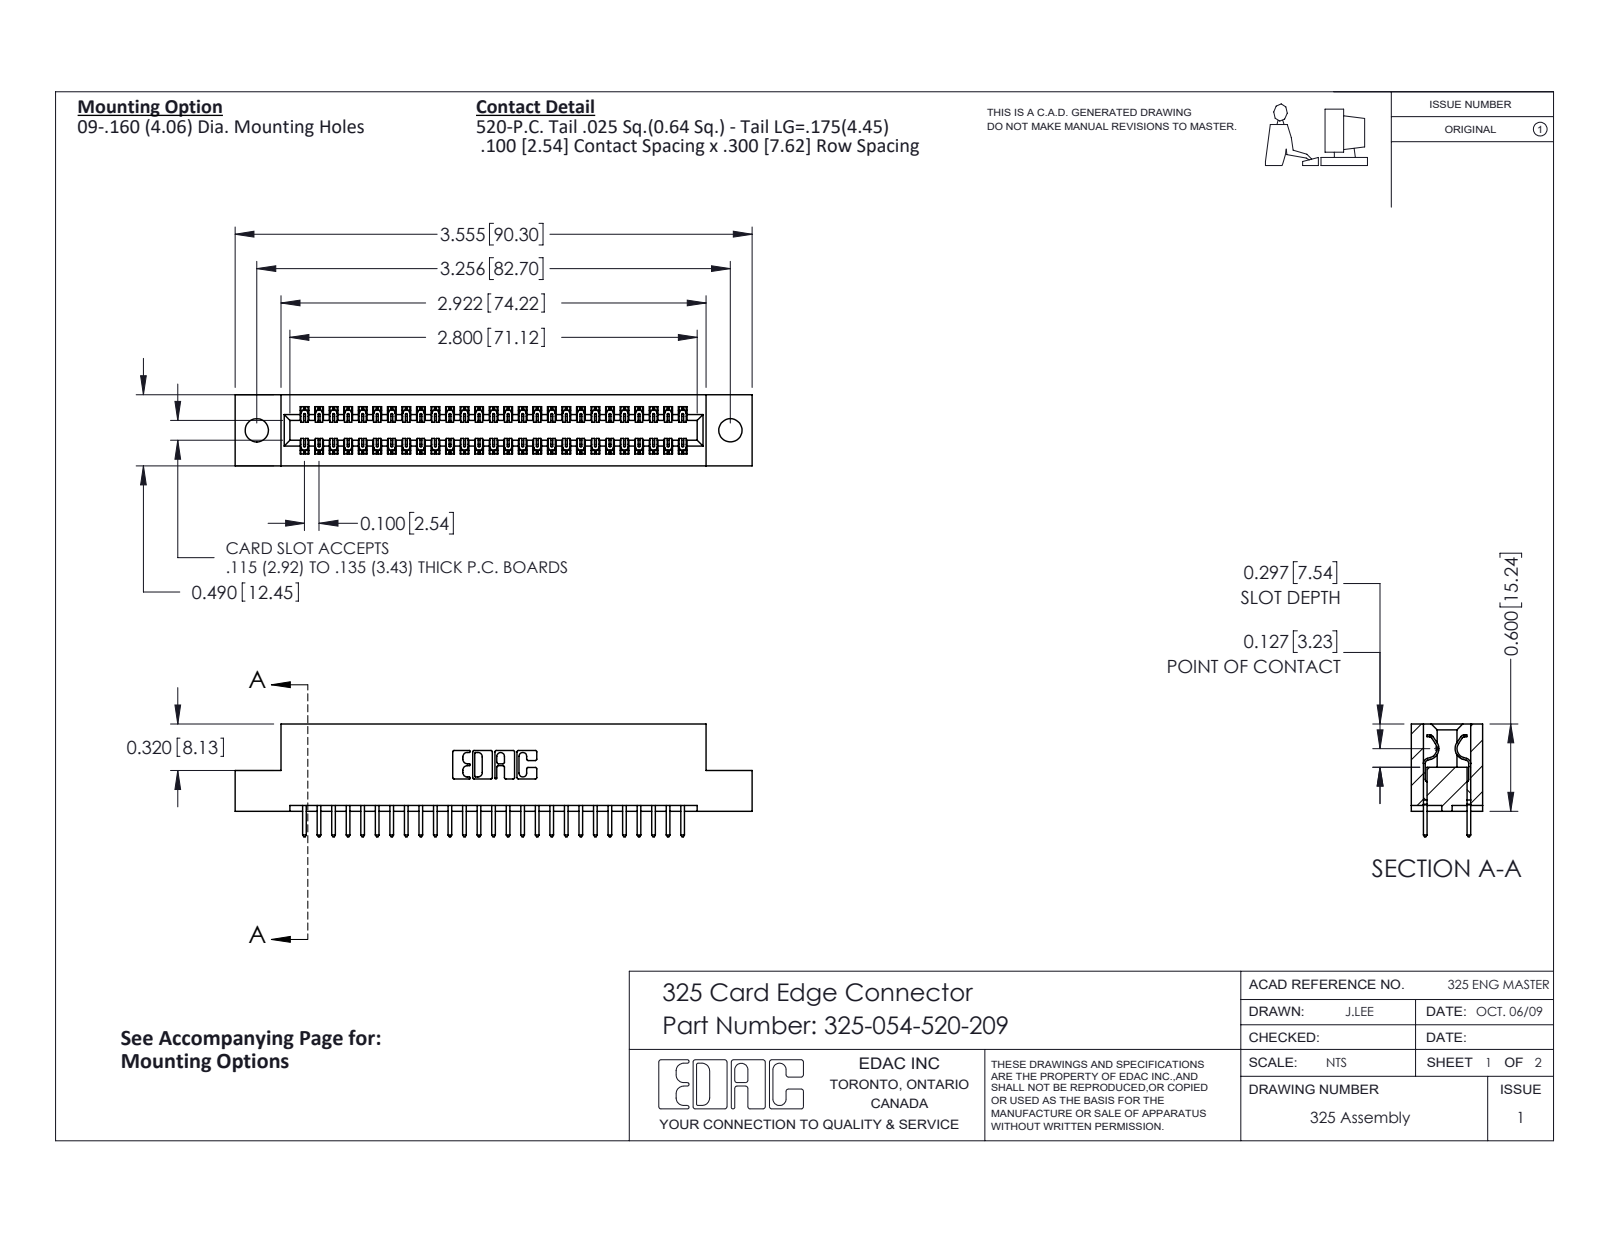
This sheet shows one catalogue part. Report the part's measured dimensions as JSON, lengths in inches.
{"part_name": "325 Part_.160 TH; 325-054-520-209; 325-292-001_325-293-120", "step_written_by": "SolidWorks 2016 (CONFIG_CONTROL_DESIGN)", "units": "inches", "bodies": {"solids": 55, "faces": 2922, "planar": 2014, "cylindrical": 908, "other": 0}, "overall_size": [3.555, 0.775, 0.49], "volume_in3": 0.689, "surface_area_in2": 20.32, "round_holes": [[0.16, 2]], "partial_cylinders_radius": [[0.006, 81], [0.01, 54], [0.01, 22], [0.007, 6], [0.031, 6], [0.026, 3], [0.014, 2], [0.022, 2]], "face_to_face_distances": [0.083, 0.407, 0.3, 0.49, 0.107, 0.383, 0.025, 0.325, 0.04, 0.1], "hole_center_spacings": [3.256]}
